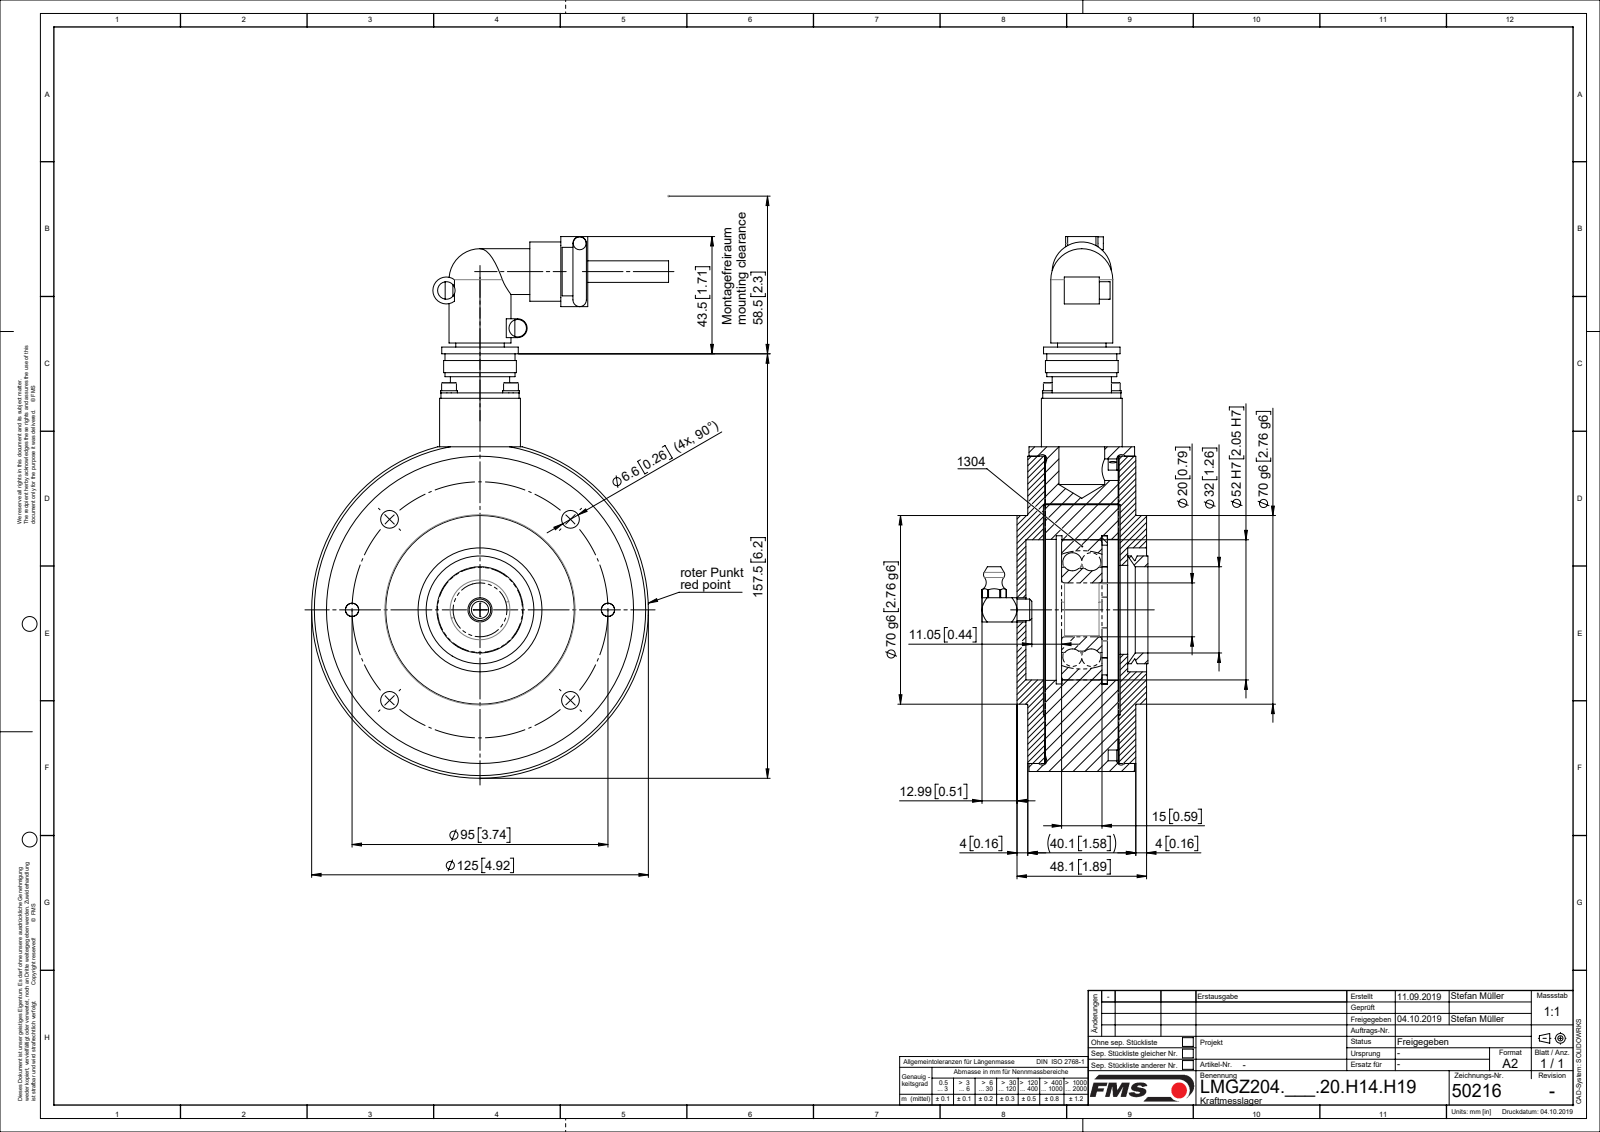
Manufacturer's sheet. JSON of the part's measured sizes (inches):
{"part_name": "ZEICHNUNG7; L50216; L4832404; L47955 (+8 more)", "step_written_by": "Mechanical Desktop 2007 (CONFIG_CONTROL_DESIGN)", "units": "inches", "bodies": {"solids": 21, "faces": 438, "planar": 129, "cylindrical": 248, "other": 61}, "overall_size": [7.913, 5.217, 2.484], "volume_in3": 30.21, "surface_area_in2": 228.9, "round_holes": [[0.26, 6], [0.102, 4], [0.126, 4], [0.134, 4], [0.138, 4], [0.197, 2], [0.433, 2], [0.342, 1], [0.787, 1], [0.906, 1], [1.22, 1], [1.299, 1]], "round_bosses_or_shafts": [[0.244, 4], [0.217, 4], [0.118, 4], [0.394, 3], [0.866, 2], [0.315, 2], [0.256, 2], [0.236, 2]], "partial_cylinders_radius": [[0.197, 9], [0.098, 2], [0.138, 1], [1.594, 1], [1.85, 1]], "face_to_face_distances": [1.073, 1.321, 0.248, 0.258, 1.331, 1.063, 1.083, 0.157, 0.415, 1.488], "hole_center_spacings": [1.87, 0.64, 0.906, 1.431, 2.645, 3.456, 1.281, 3.741]}
